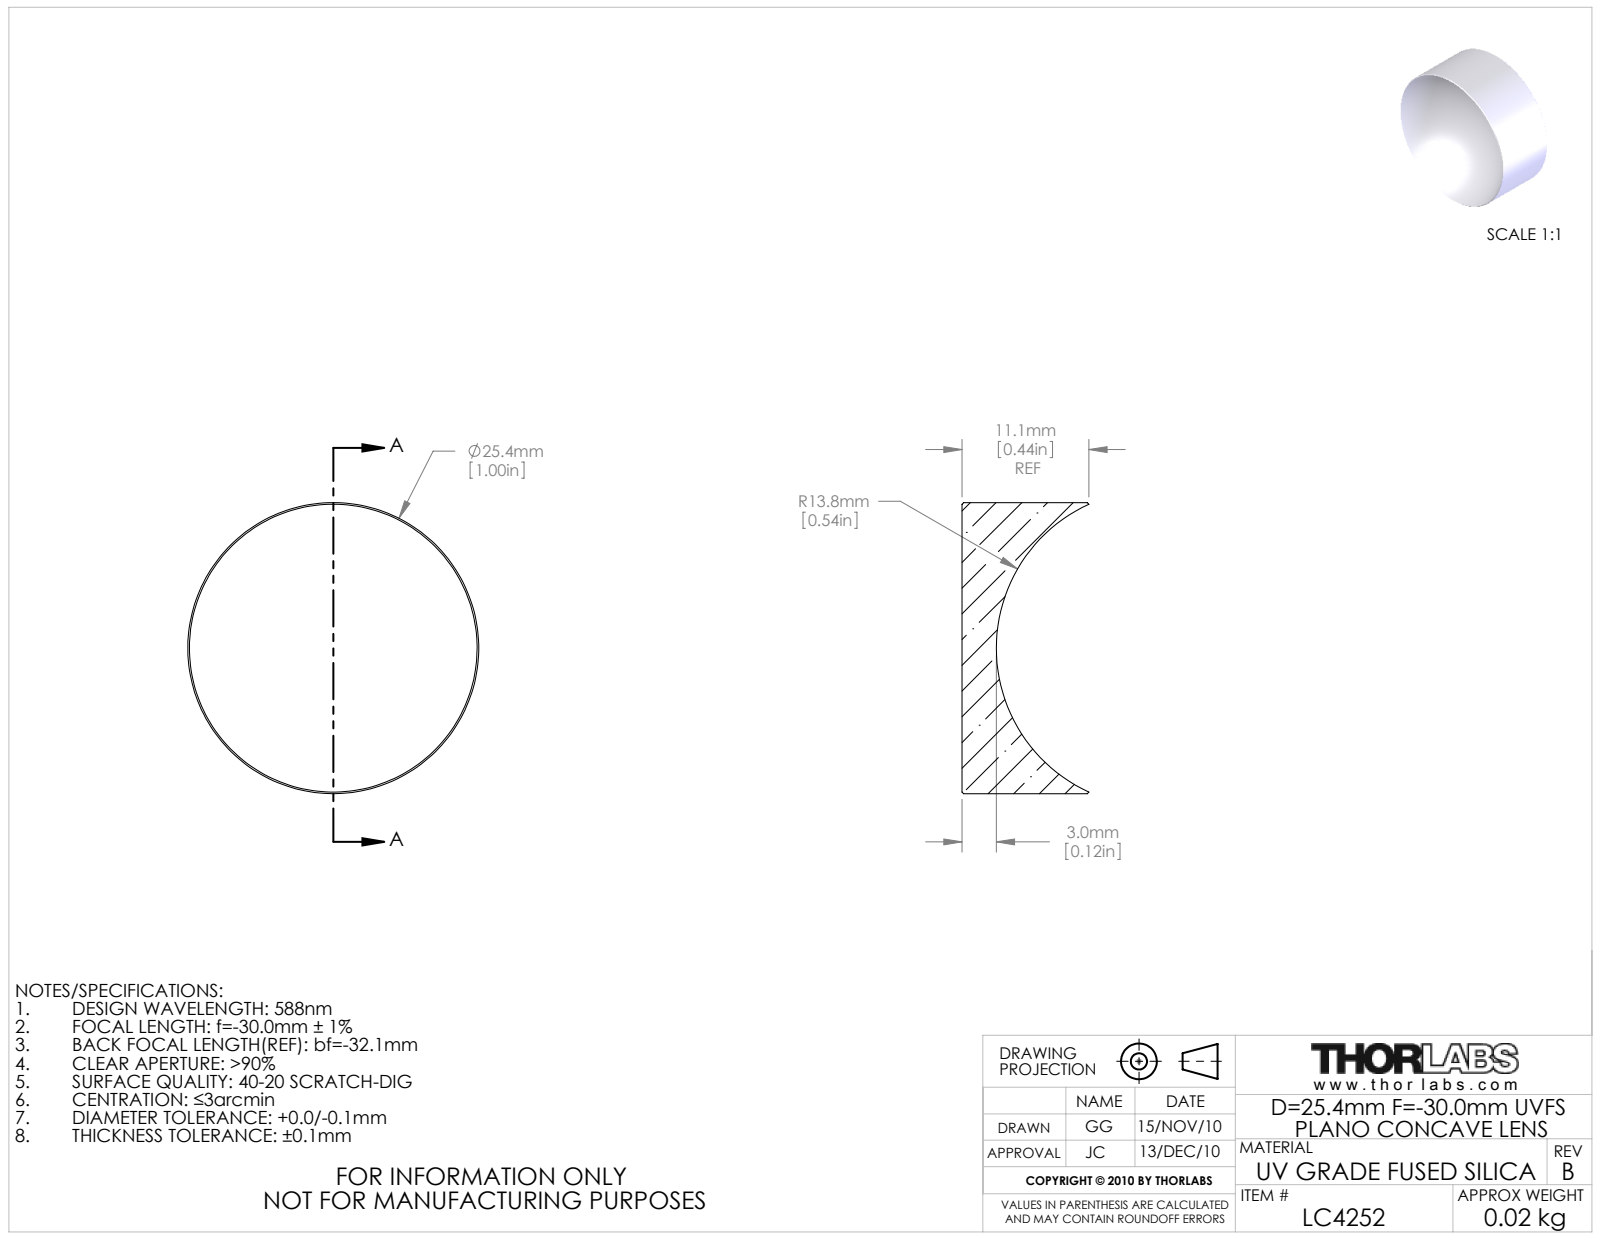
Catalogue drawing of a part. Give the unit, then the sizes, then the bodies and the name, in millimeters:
Units: millimetres
Overall size (bounding box): 25.4 × 25.4 × 11.08
Round bosses / shafts (diameter × count): ⌀25.4 ×1
Volume: 3 335 mm³ · Surface area: 2 089 mm²
Bodies: 1 solid, 9 faces (1 planar, 2 cylindrical, 6 other)
Part name (STEP PRODUCT): 3501-E0W
STEP written by: SolidWorks 2009 (AUTOMOTIVE_DESIGN)
